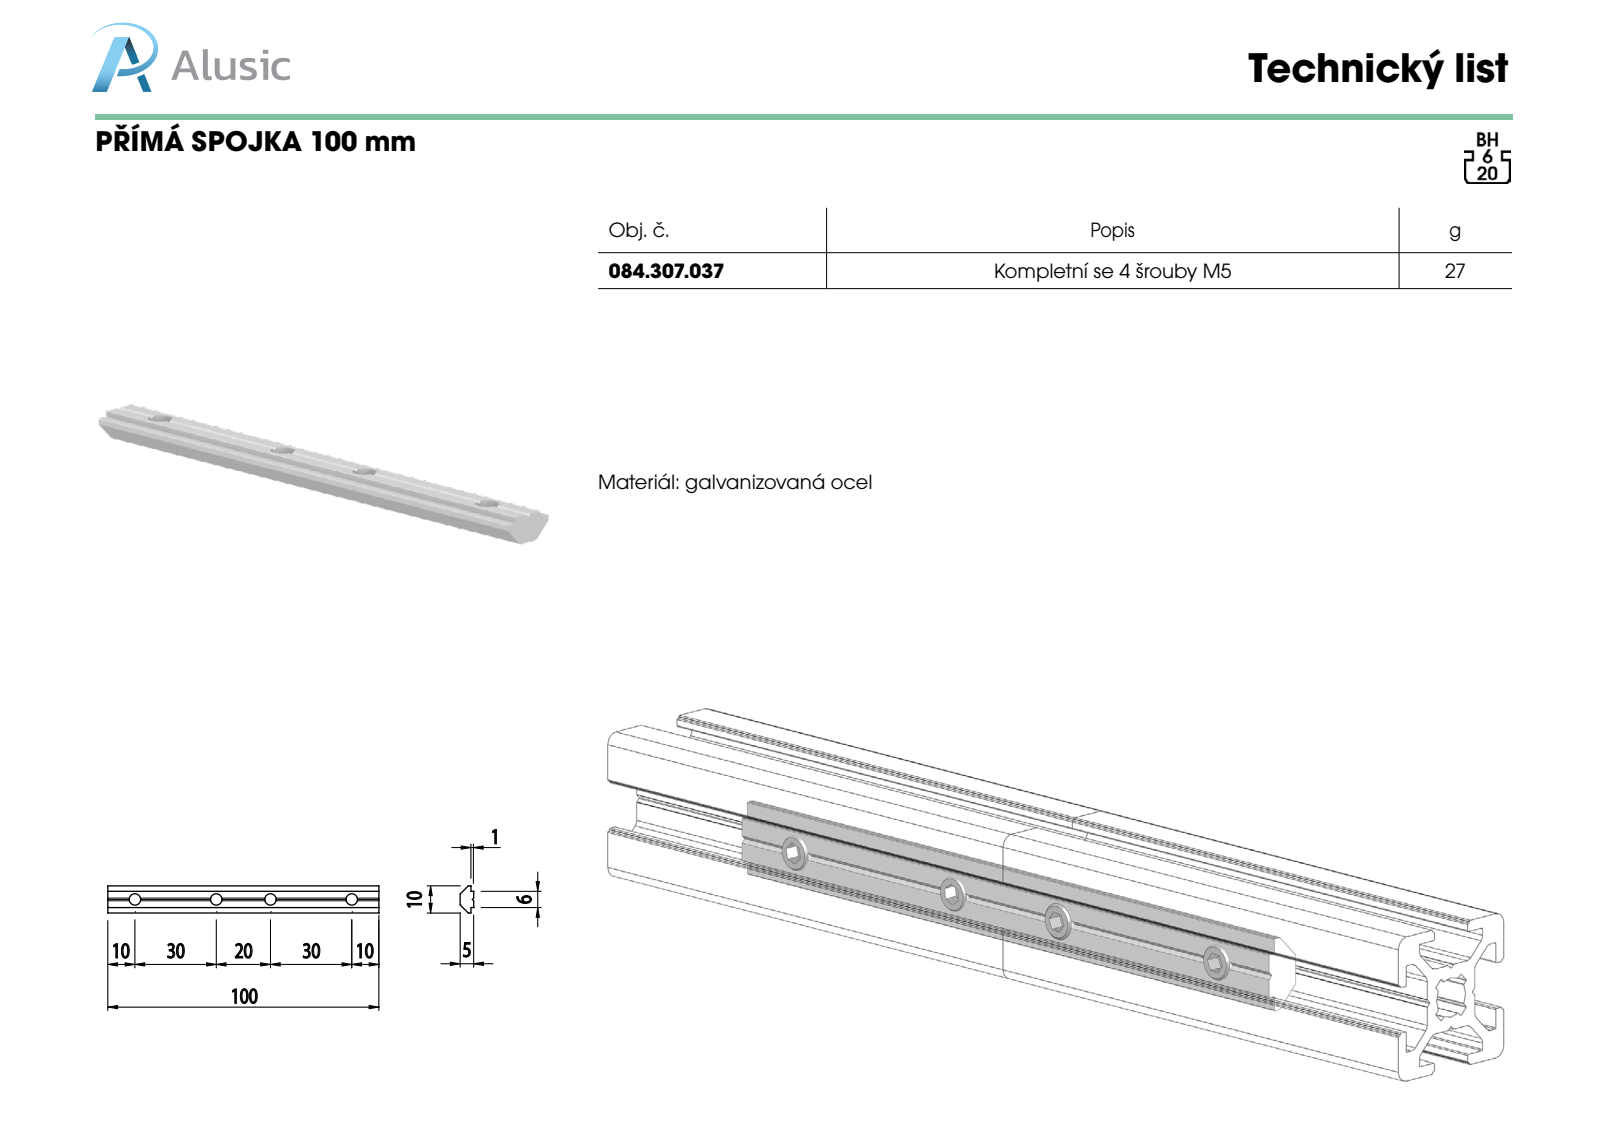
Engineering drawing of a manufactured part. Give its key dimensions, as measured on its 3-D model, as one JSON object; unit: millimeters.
{"part_name": "084.307.037", "step_written_by": "SolidWorks 2012 (CONFIG_CONTROL_DESIGN)", "units": "millimeters", "bodies": {"solids": 1, "faces": 39, "planar": 27, "cylindrical": 12, "other": 0}, "overall_size": [100, 10, 5], "volume_mm3": 3401, "surface_area_mm2": 2889, "round_holes": [[4.2, 4]], "partial_cylinders_radius": [[0.1, 4]], "face_to_face_distances": [1, 4, 5, 2, 8, 4.6, 10, 6, 100], "hole_center_spacings": [30, 50, 20, 80]}
